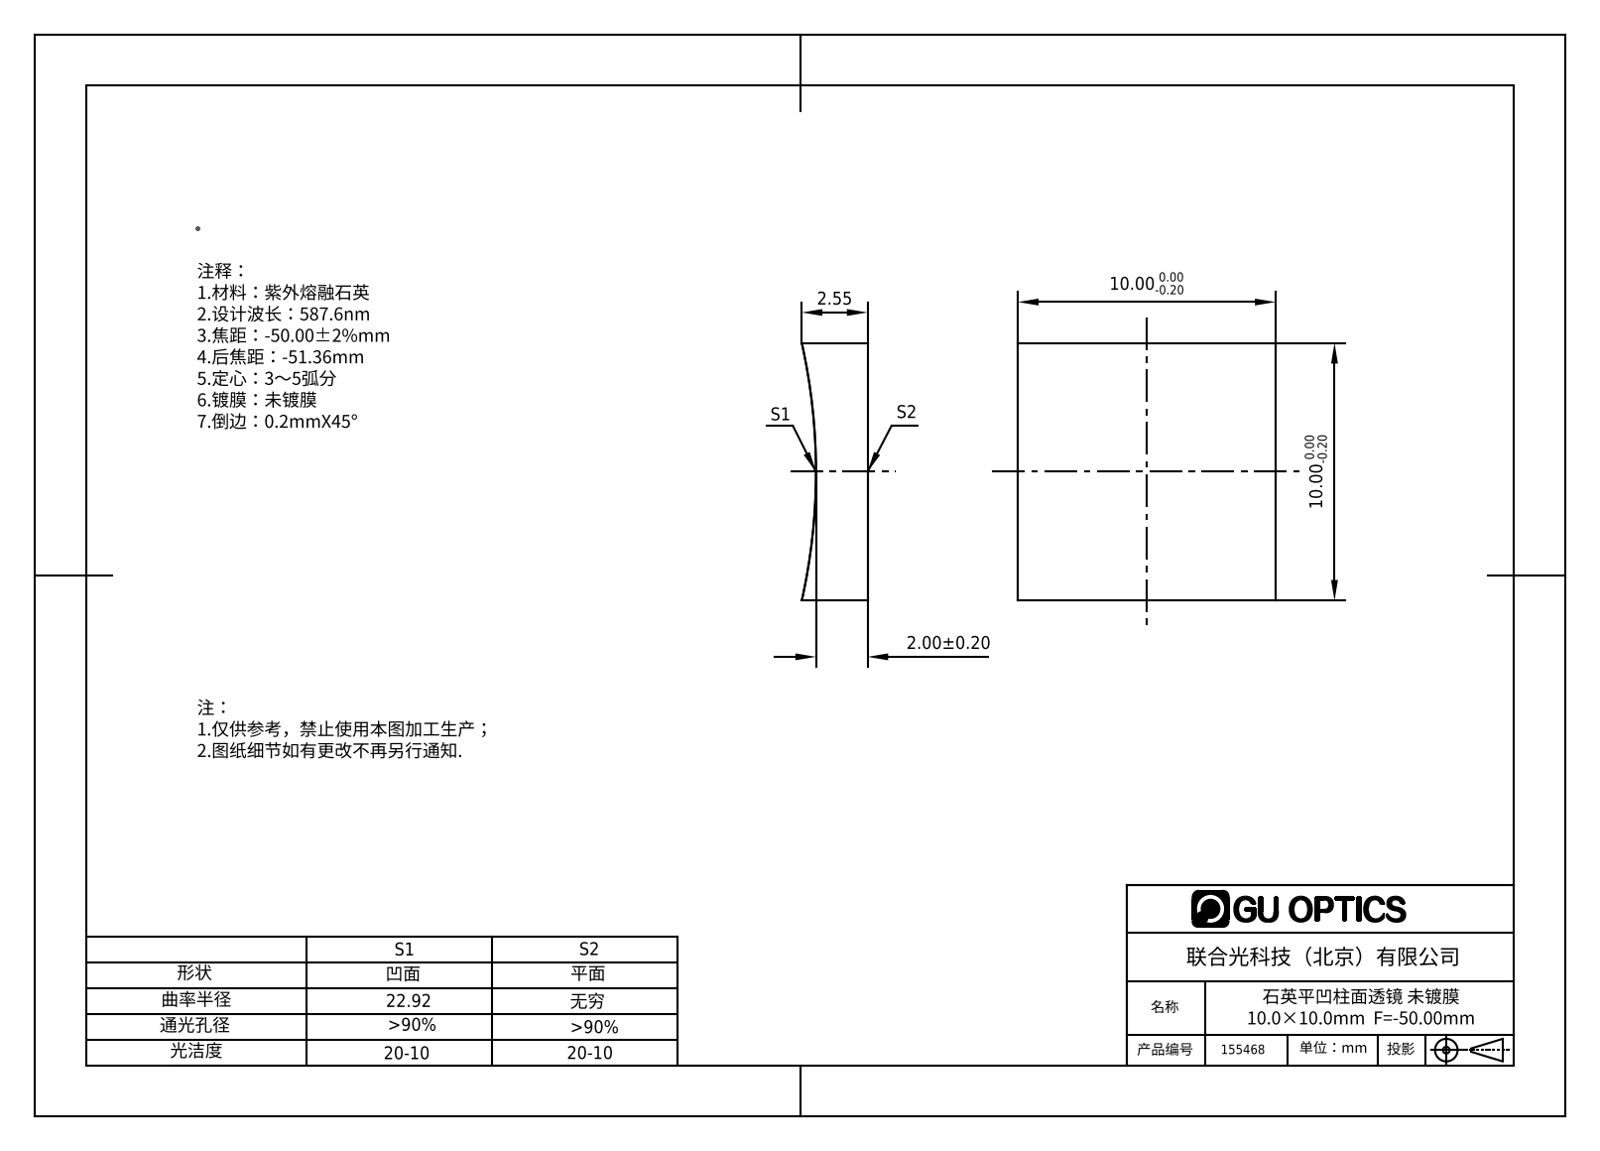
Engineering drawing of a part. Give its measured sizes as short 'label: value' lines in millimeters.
name: 155468
written by: SolidWorks 2016 (AUTOMOTIVE_DESIGN)
unit: mm
bodies: 1 solid, 6 faces (5 planar, 1 cylindrical, 0 other)
size: 10 × 10 × 2.55
volume: 218 mm³; area: 296 mm²
rounds: 1× R22.92
face distances: 10
